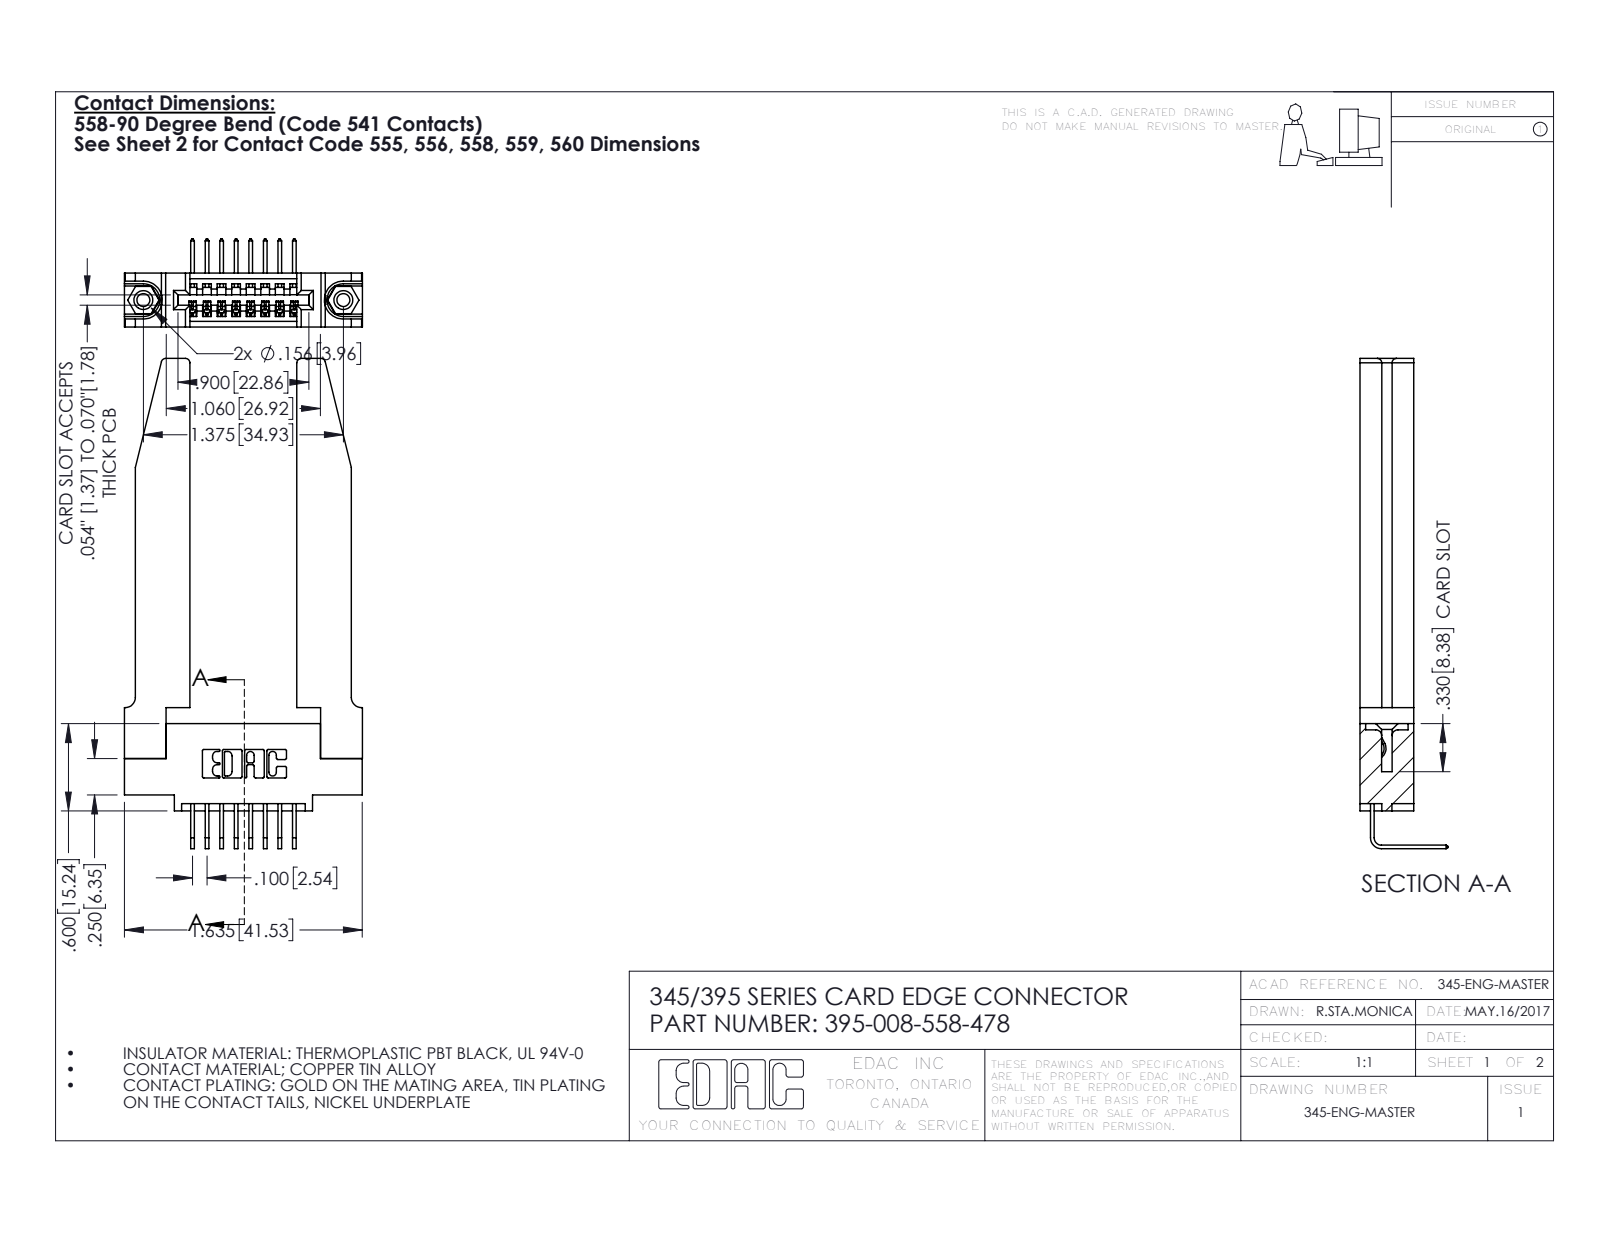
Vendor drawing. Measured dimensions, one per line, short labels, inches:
name: 395-008-558-478; 345 Part_0.110 Offset - 0.156 Dia-TH; 345-250-001_345-250-001-102; 345-220-078_345-220-078 (+1 more)
written by: SolidWorks 2016 (CONFIG_CONTROL_DESIGN)
unit: in
bodies: 13 solids, 844 faces (562 planar, 230 cylindrical, 52 other)
size: 3.369 × 1.636 × 0.605
volume: 0.695 in³; area: 17.72 in²
holes: 2× ⌀0.089, 2× ⌀0.125, 2× ⌀0.156, 1× ⌀0.064
bosses: 2× ⌀0.155
rounds: 22× R0.01, 16× R0.006, 8× R0.03, 6× R0.007, 6× R0.031, 3× R0.026, 2× R0.031, 2× R0.04
face distances: 0.37, 0.15, 0.072, 0.22, 0.148, 0.298, 0.735, 0.077, 0.071, 0.055
hole spacings: 0.27, 1.144, 1.375
